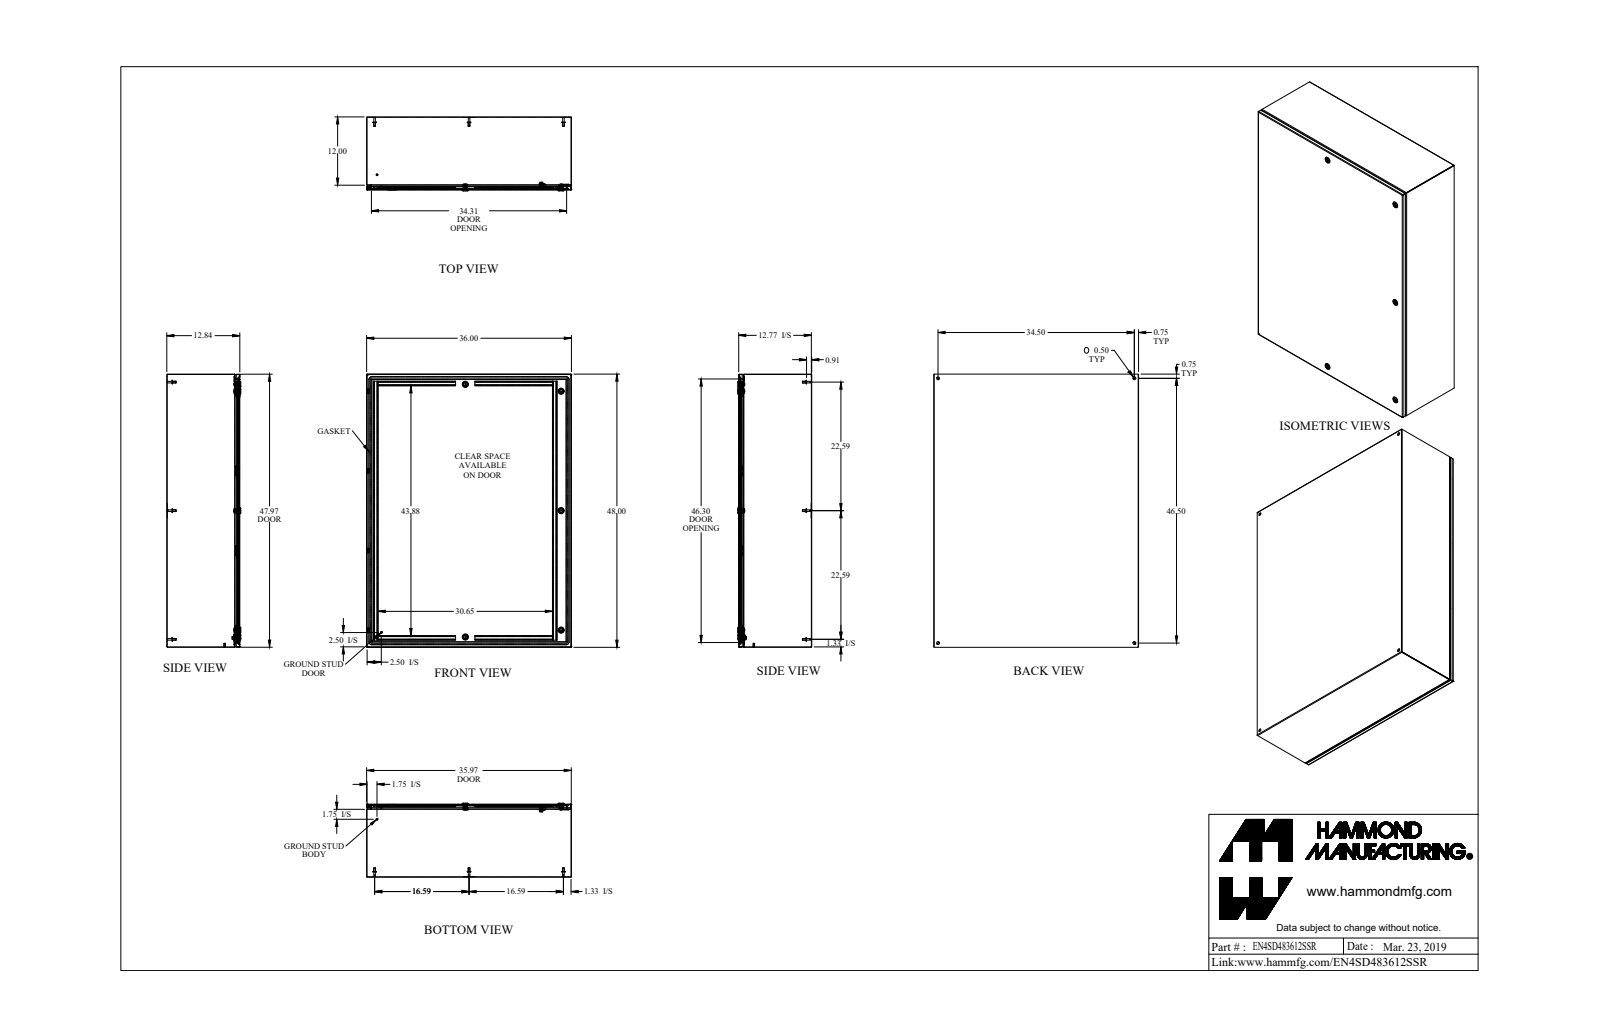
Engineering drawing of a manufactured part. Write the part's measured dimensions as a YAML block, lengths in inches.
part_name: "EN4SD483612SSR"
step_written_by: "SolidWorks 2018 (AUTOMOTIVE_DESIGN)"
units: inches
bodies: {solids: 66, faces: 1715, planar: 896, cylindrical: 544, other: 275}
overall_size: [48, 36, 13.002]
volume: 448.4
surface_area: 12642
round_holes:
  - {diameter: 0.5, count: 9}
  - {diameter: 0.197, count: 5}
  - {diameter: 0.387, count: 5}
  - {diameter: 0.63, count: 5}
  - {diameter: 0.768, count: 5}
  - {diameter: 0.172, count: 1}
  - {diameter: 0.196, count: 1}
  - {diameter: 0.24, count: 1}
  - {diameter: 0.242, count: 1}
  - {diameter: 0.275, count: 1}
  - {diameter: 0.375, count: 1}
round_bosses_or_shafts:
  - {diameter: 0.313, count: 10}
  - {diameter: 0.625, count: 9}
  - {diameter: 0.275, count: 8}
  - {diameter: 1.1, count: 5}
  - {diameter: 0.625, count: 5}
  - {diameter: 0.236, count: 5}
  - {diameter: 0.785, count: 3}
  - {diameter: 0.525, count: 3}
partial_cylinders:
  - {radius: 0.048, count: 32}
  - {radius: 0.01, count: 24}
  - {radius: 0.036, count: 18}
  - {radius: 0.108, count: 18}
  - {radius: 0.062, count: 17}
  - {radius: 0.094, count: 10}
  - {radius: 0.125, count: 10}
  - {radius: 0.016, count: 9}
face_to_face_distances: [0.072, 12.77, 12.698, 12.842, 35.928, 35.856, 36, 0.072, 47.856, 47.928]
hole_center_spacings: [16.622, 16.881, 17.943, 23.275, 27.854, 33.504, 34.5, 40.718]
